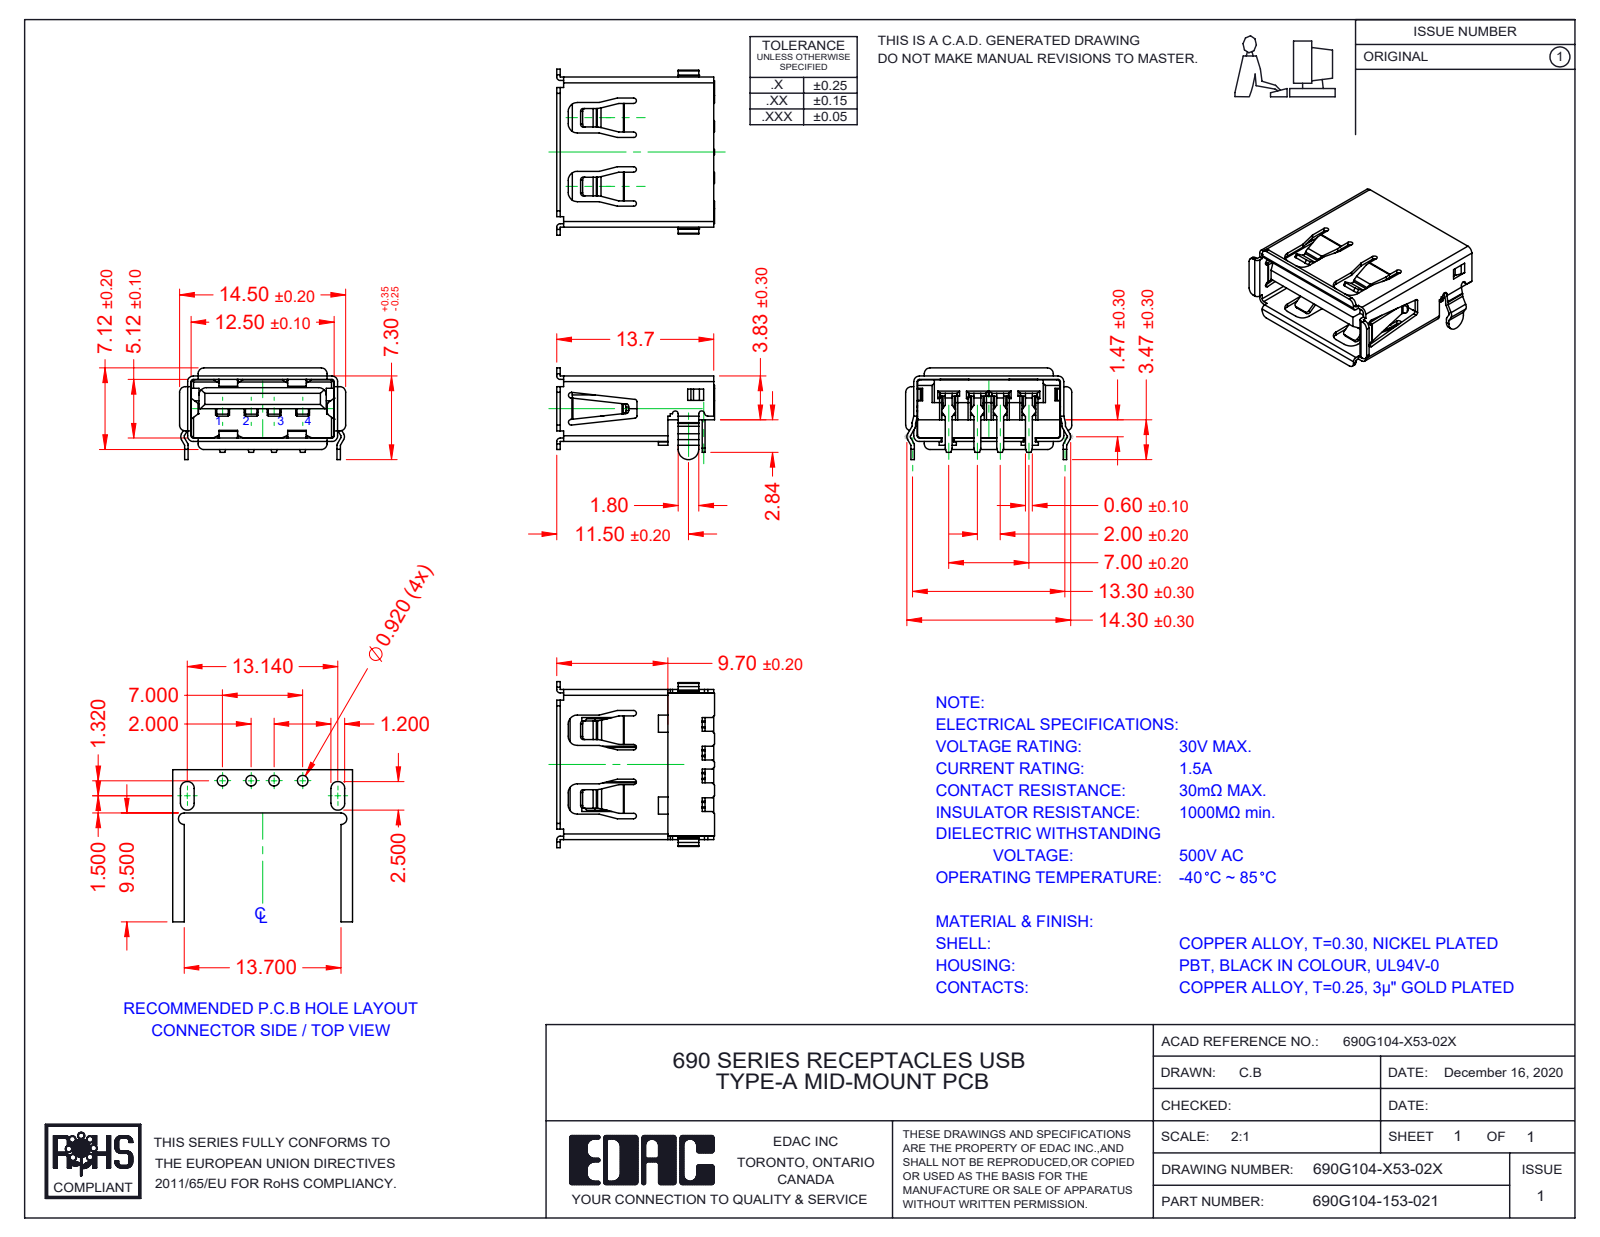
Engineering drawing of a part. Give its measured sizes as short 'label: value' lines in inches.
name: 690G104-153-021; Insulator 690G104-X53-02X_Black; Contact 690G104-X53-02X; Shell 690G104-X53-02X
written by: SolidWorks 2020 (AUTOMOTIVE_DESIGN)
unit: in
bodies: 6 solids, 743 faces (561 planar, 166 cylindrical, 16 other)
size: 0.571 × 0.543 × 0.315
volume: 0.025 in³; area: 2.72 in²
rounds: 22× R0.01, 20× R0.02, 15× R0.012, 14× R0.008, 10× R0.004, 5× R0.035, 4× R0.024, 4× R0.031
face distances: 0.213, 0.101, 0.113, 0.02, 0.225, 0.048, 0.504, 0.202, 0.06, 0.04
